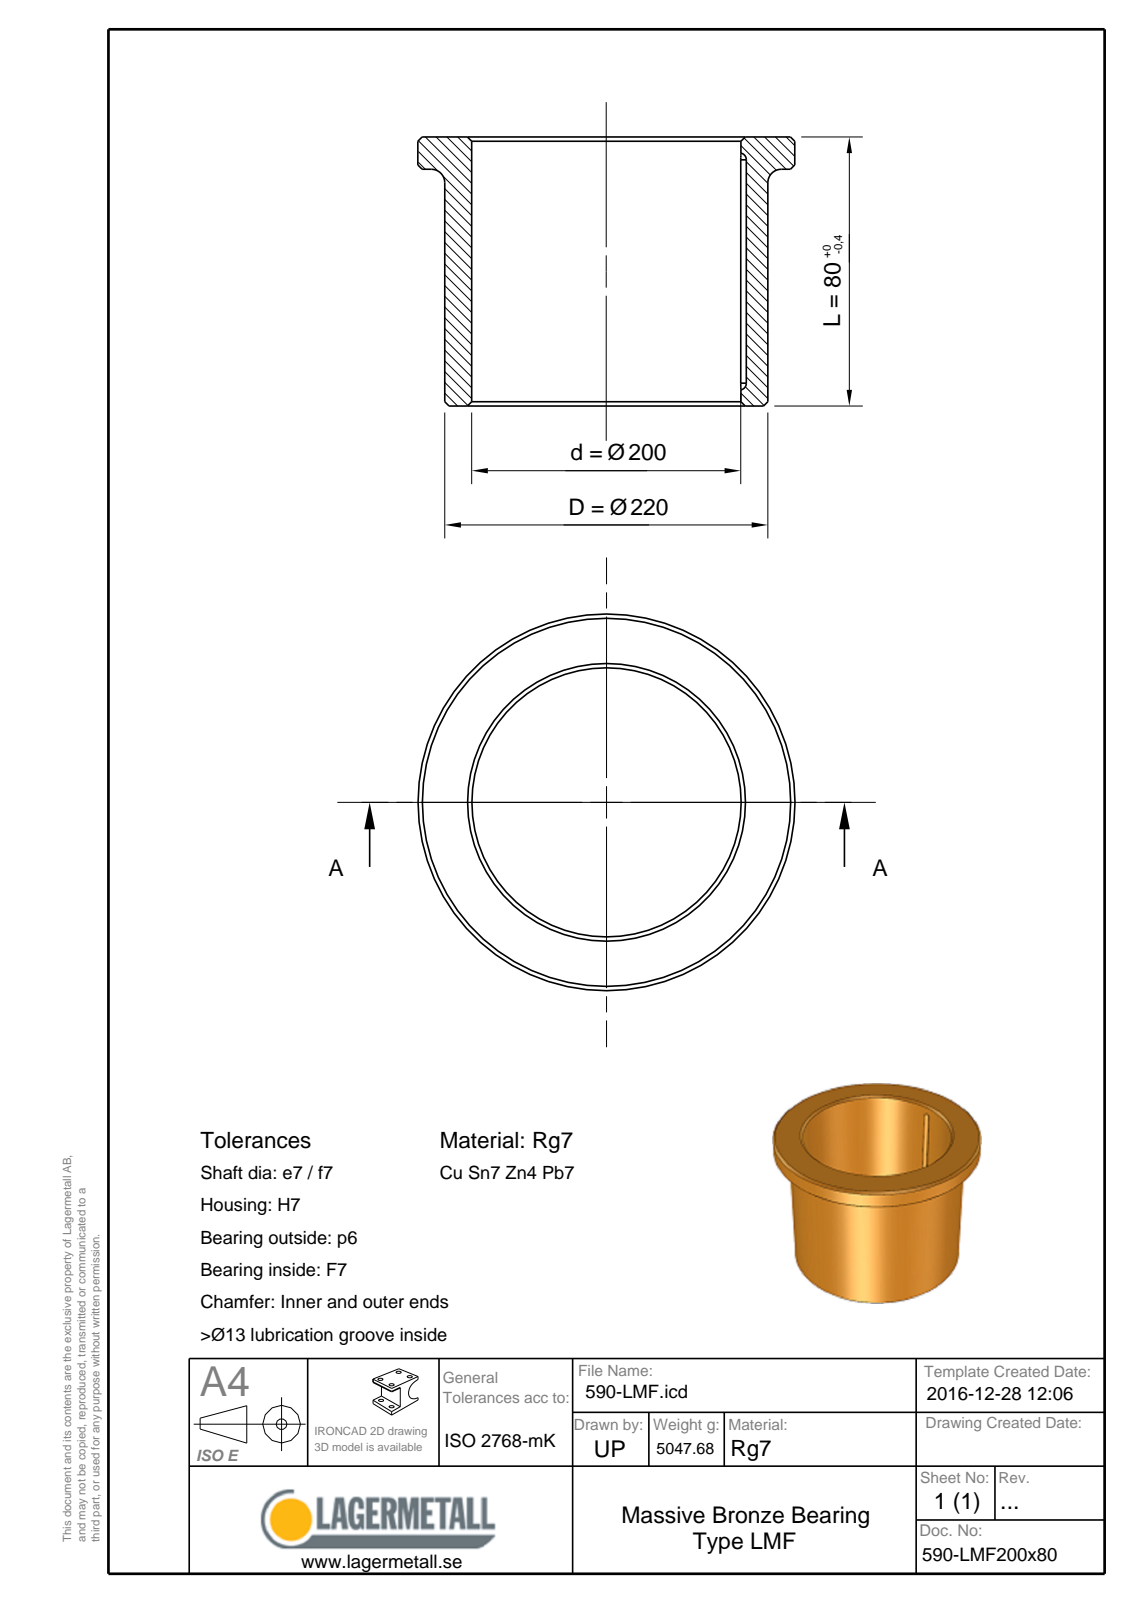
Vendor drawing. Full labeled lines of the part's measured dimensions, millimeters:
Part name (STEP PRODUCT): 590-LMF200x80
STEP written by: Spatial InterOp 3D (CONFIG_CONTROL_DESIGN)
Units: millimetres
Bodies: 1 solid, 16 faces (6 planar, 5 cylindrical, 5 other)
Overall size (bounding box): 235 × 235 × 80
Volume: 573 600 mm³ · Surface area: 126 298 mm²
Round holes (diameter × count): ⌀200 ×1
Round bosses / shafts (diameter × count): ⌀235 ×1, ⌀220 ×1
Partial cylindrical surfaces — rounded edges, fillets, slot ends (radius × count): R2.75 ×2
Main face-to-face distances: 80, 70, 10, 5.5
